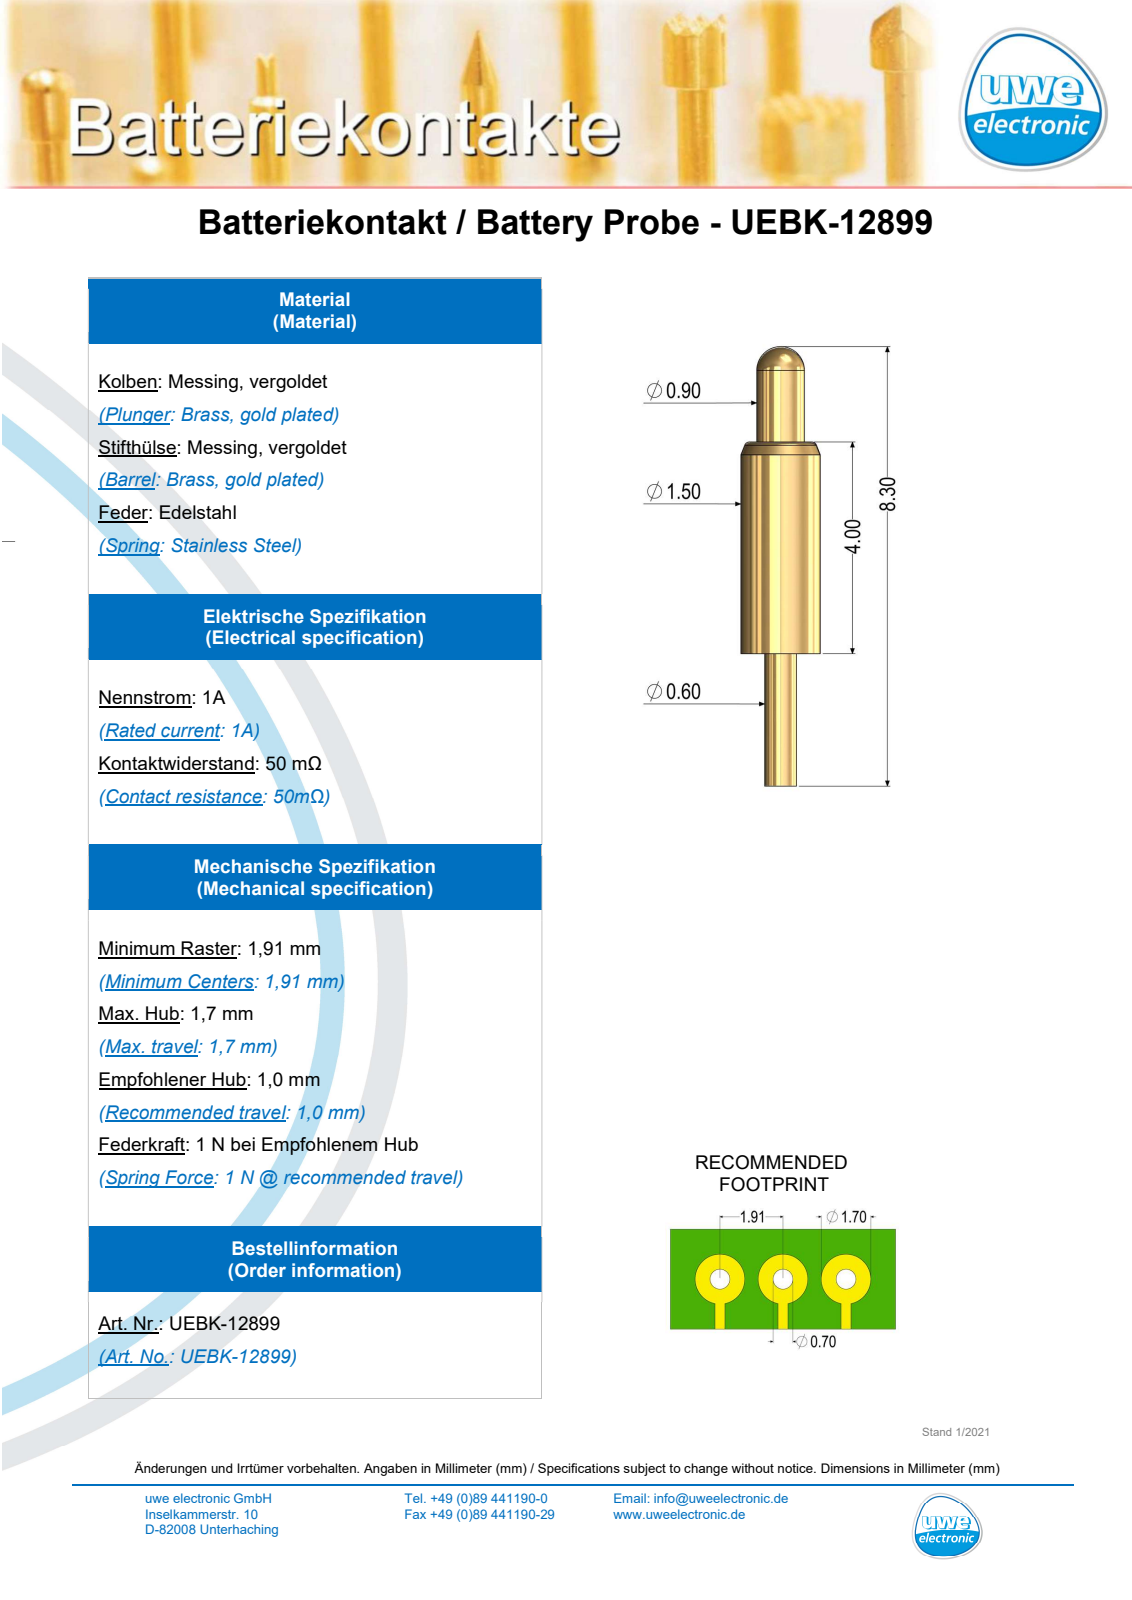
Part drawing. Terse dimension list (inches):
name: UEBK-12899_2017_08_28
written by: SolidWorks 2017 (AUTOMOTIVE_DESIGN)
unit: in
bodies: 1 solid, 15 faces (3 planar, 6 cylindrical, 6 other)
size: 0.327 × 0.059 × 0.059
volume: 0.001 in³; area: 0.048 in²
bosses: 1× ⌀0.059, 1× ⌀0.035, 1× ⌀0.024
face distances: 0.157, 0.256, 0.098
